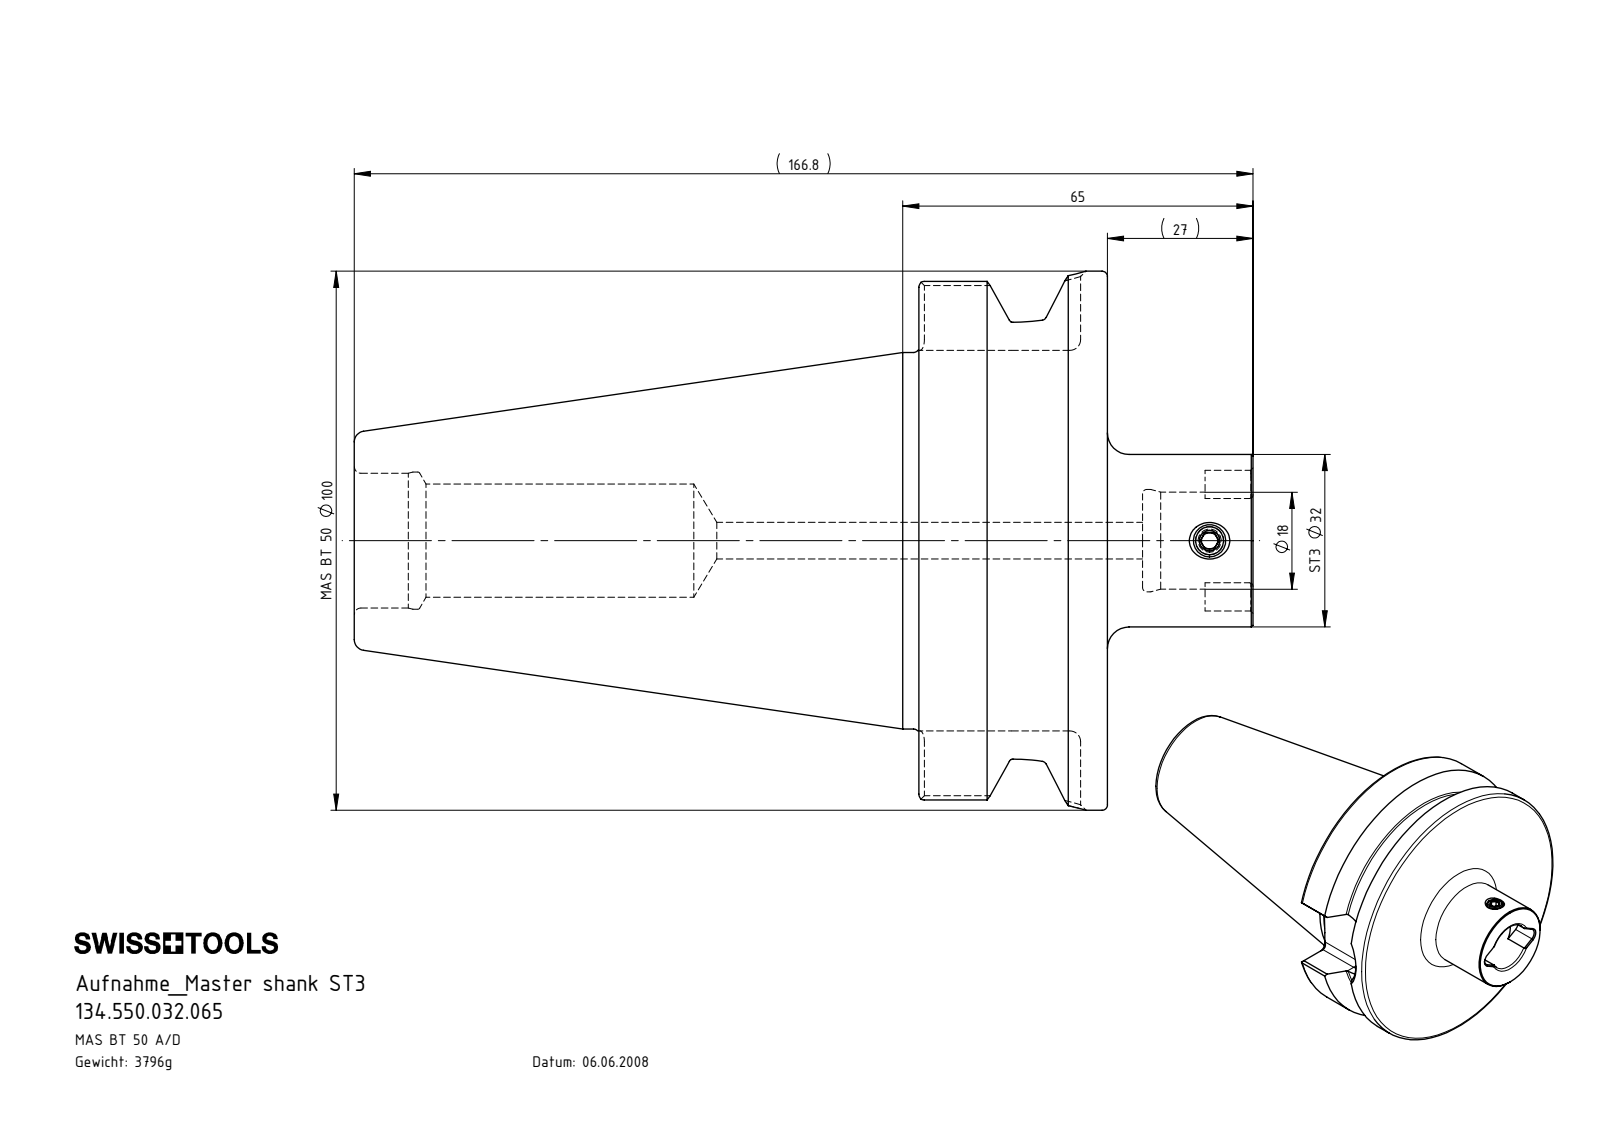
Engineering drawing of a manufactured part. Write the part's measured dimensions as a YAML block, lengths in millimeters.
part_name: "BT5.ST3.K01.065; BT5-ST3.K01.065_B; ST3-ER1.001.008_A"
step_written_by: "SolidWorks 2017 (AUTOMOTIVE_DESIGN)"
units: millimeters
bodies: {solids: 2, faces: 109, planar: 42, cylindrical: 28, other: 39}
overall_size: [166.8, 100, 100]
volume: 483601
surface_area: 54413
round_holes:
  - {diameter: 3, count: 1}
  - {diameter: 5.25, count: 1}
  - {diameter: 6.8, count: 1}
  - {diameter: 18, count: 1}
  - {diameter: 19, count: 1}
  - {diameter: 21, count: 1}
  - {diameter: 25, count: 1}
  - {diameter: 25.45, count: 1}
round_bosses_or_shafts:
  - {diameter: 100, count: 1}
  - {diameter: 85, count: 1}
  - {diameter: 69.85, count: 1}
  - {diameter: 32, count: 1}
  - {diameter: 6, count: 1}
partial_cylinders:
  - {radius: 2, count: 8}
  - {radius: 2.5, count: 2}
  - {radius: 12.85, count: 1}
face_to_face_distances: [35, 70.6, 104.8, 139.8, 166.8, 62, 27, 25.7, 146.3, 41.5]
